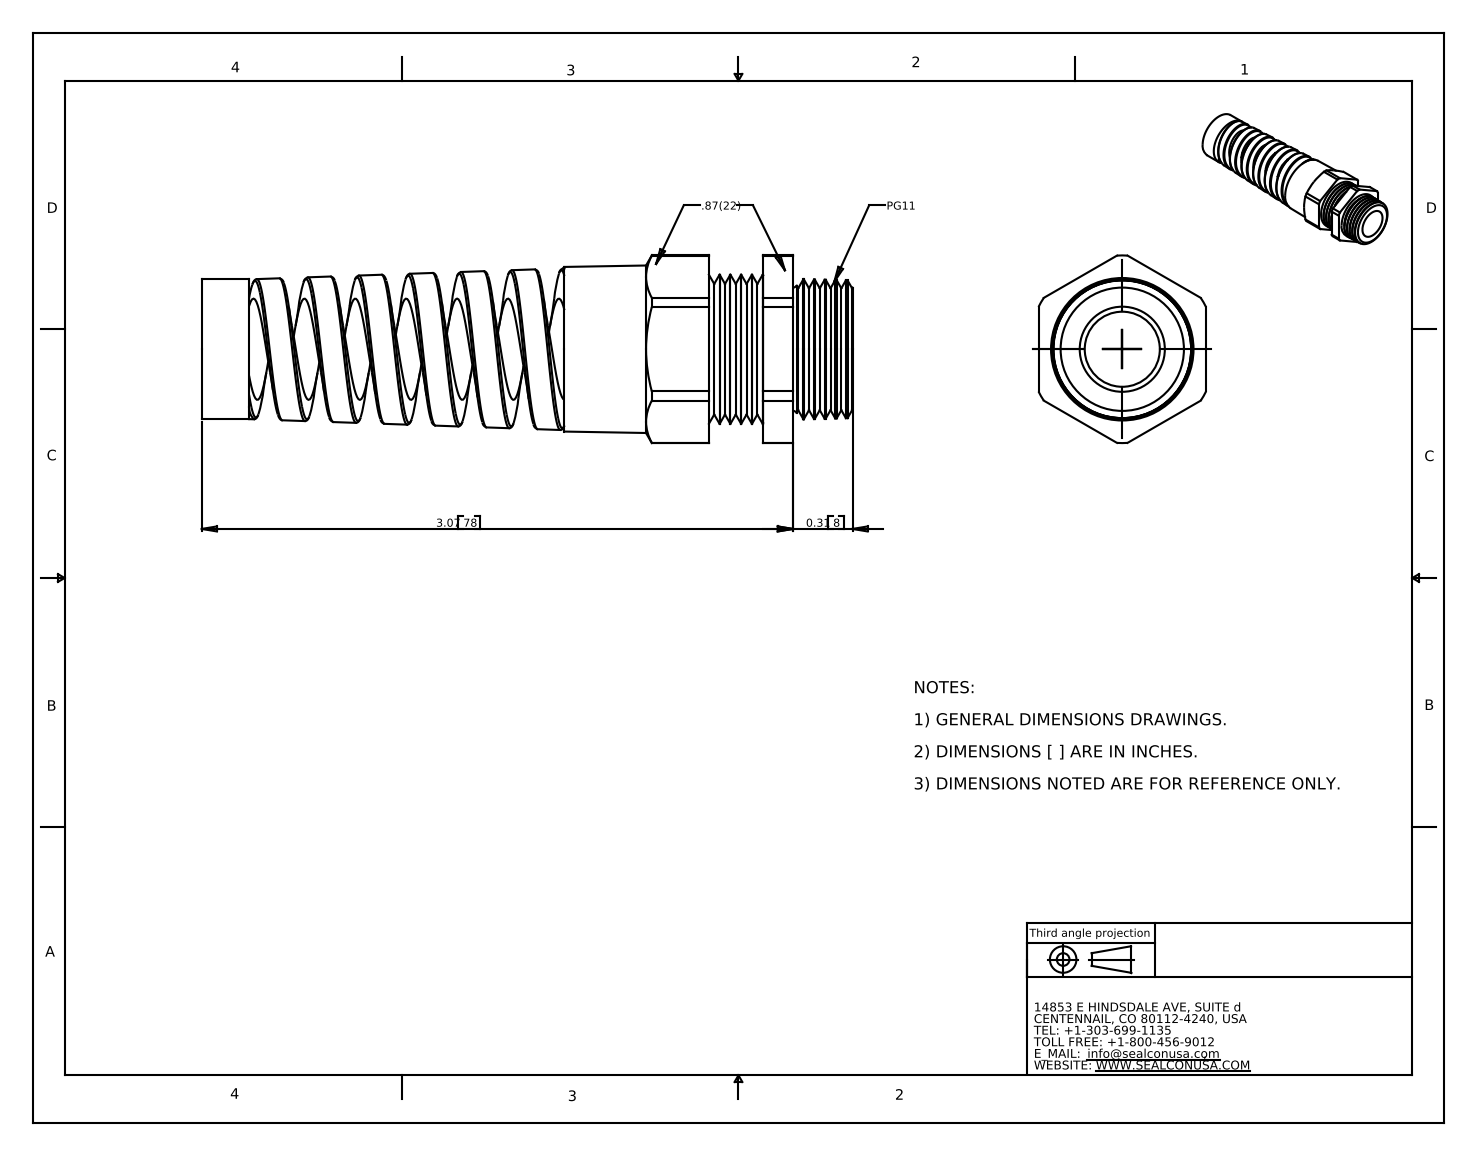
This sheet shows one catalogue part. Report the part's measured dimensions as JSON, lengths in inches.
{"part_name": "CF11AA-BK", "step_written_by": "SolidWorks 2007 (CONFIG_CONTROL_DESIGN)", "units": "inches", "bodies": {"solids": 1, "faces": 153, "planar": 19, "cylindrical": 42, "other": 92}, "overall_size": [3.38, 0.974, 0.87], "volume_in3": 0.877, "surface_area_in2": 16.71, "round_holes": [[0.39, 1], [0.526, 1]], "round_bosses_or_shafts": [[0.774, 1], [0.726, 1]], "partial_cylinders_radius": [[0.487, 1]], "face_to_face_distances": [0.87, 1.186, 1.884, 3.07, 2.634, 0.75, 0.436, 2.916, 1.032, 0.281]}
